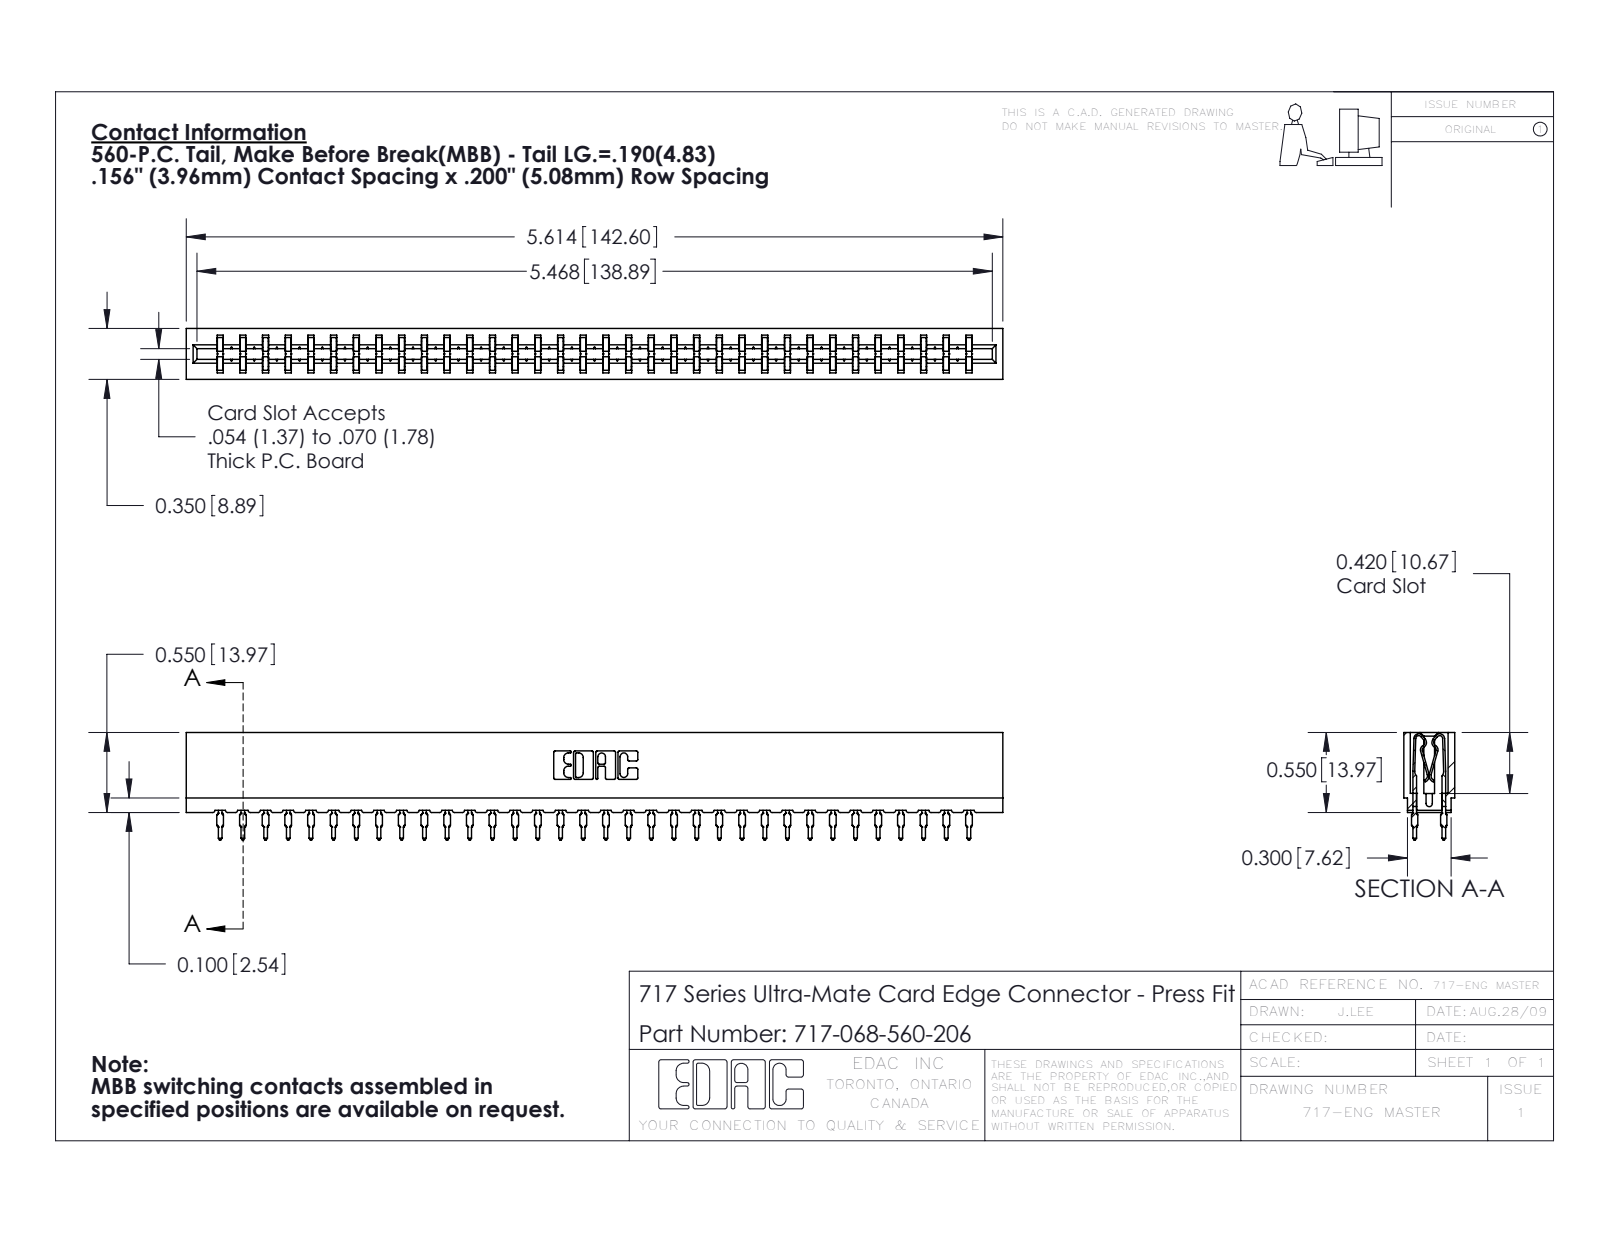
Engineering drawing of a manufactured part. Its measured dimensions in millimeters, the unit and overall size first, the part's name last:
Units: millimetres
Overall size (bounding box): 142.6 × 18.8 × 8.9
Partial cylindrical surfaces — rounded edges, fillets, slot ends (radius × count): R0.5 ×136, R0.4 ×68, R0.3 ×22, R0.1 ×8, R0.3 ×8, R0.2 ×6, R0.8 ×6, R0.7 ×3
Main face-to-face distances: 5.4, 3.5, 8.9, 1.6, 7.3, 1.9, 3.8, 1.9, 4, 1.1
Volume: 12 600 mm³ · Surface area: 20 430 mm²
Bodies: 69 solids, 6826 faces (3556 planar, 1502 cylindrical, 1768 other)
Part name (STEP PRODUCT): 745-292-001_560; 717 Part_Insulator Option - 06; 717-068-560-206
STEP written by: SolidWorks 2016 (CONFIG_CONTROL_DESIGN)
